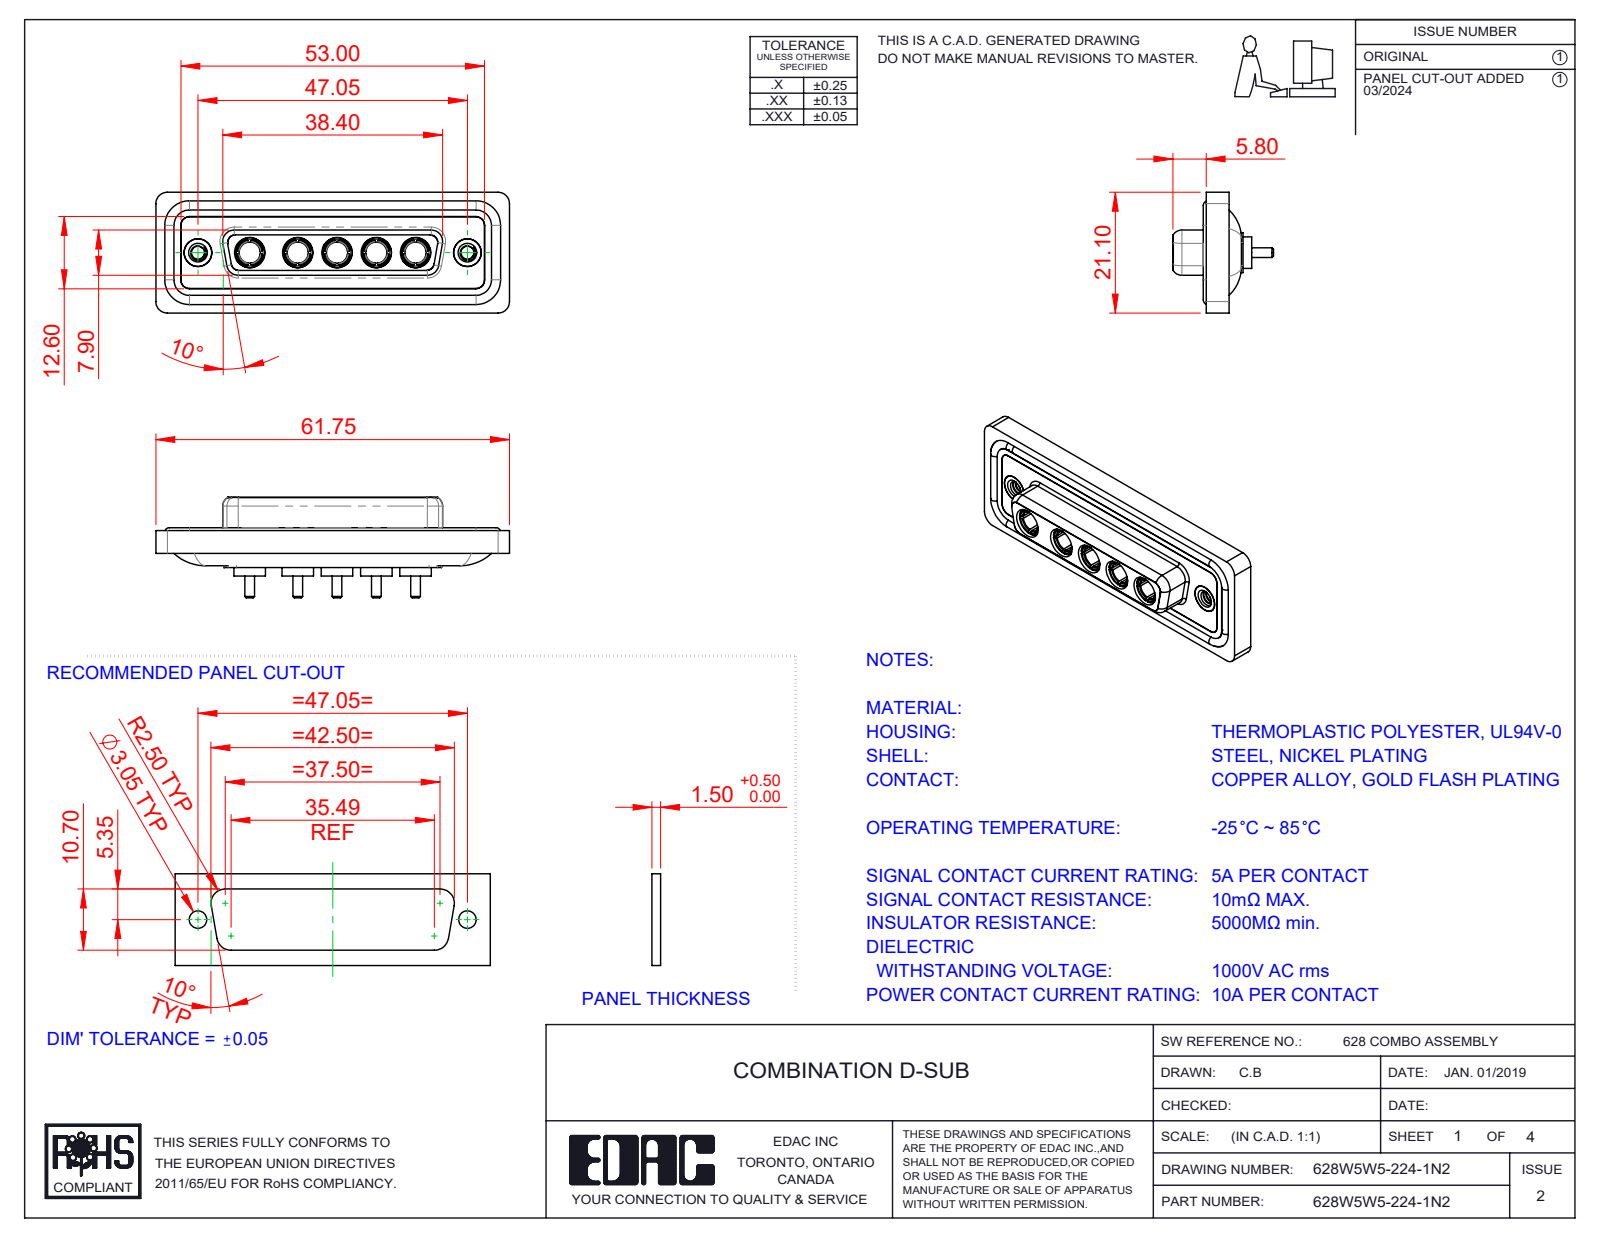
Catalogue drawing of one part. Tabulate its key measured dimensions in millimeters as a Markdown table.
| quantity | value |
| --- | --- |
| part name | 628Combo Housing_5W5; 628W5W5-224-1N2; 628Combo Threaded Rivet_2; 628Combo Shell Front_25 Contacts (+3 more) |
| STEP written by | SolidWorks 2023 (CONFIG_CONTROL_DESIGN) |
| units | millimeters |
| bodies | 17 solids, 756 faces (250 planar, 303 cylindrical, 203 other) |
| overall size | 61.75 × 21.1 × 17.55 |
| volume | 8 099 mm³ |
| surface area | 13 352 mm² |
| round holes (diameter × count) | 4.85 × 7, 3.7 × 5, 5.3 × 5, 2.26 × 2, 4 × 2, 4.05 × 2, 5 × 2 |
| round bosses / shafts (diameter × count) | 5.5 × 5, 5.2 × 5, 4.96 × 5, 4.75 × 5, 3.75 × 5, 1.7 × 5, 1.6 × 4, 4.95 × 2 |
| partial cylindrical surfaces (radius × count) | 1.5 × 22, 2 × 18, 1.35 × 8, 1.6 × 8, 2.1 × 5, 0.25 × 4, 0.5 × 4, 0.6 × 4 |
| main face-to-face distances | 0.4, 1.8, 7.45, 5.65, 0.5, 7.05, 6.6, 1.6, 1.1, 1.5 |
| hole center spacings | 6.86, 9.04, 13.72, 38.01, 8.39, 15.25, 15.9, 17.43 |
